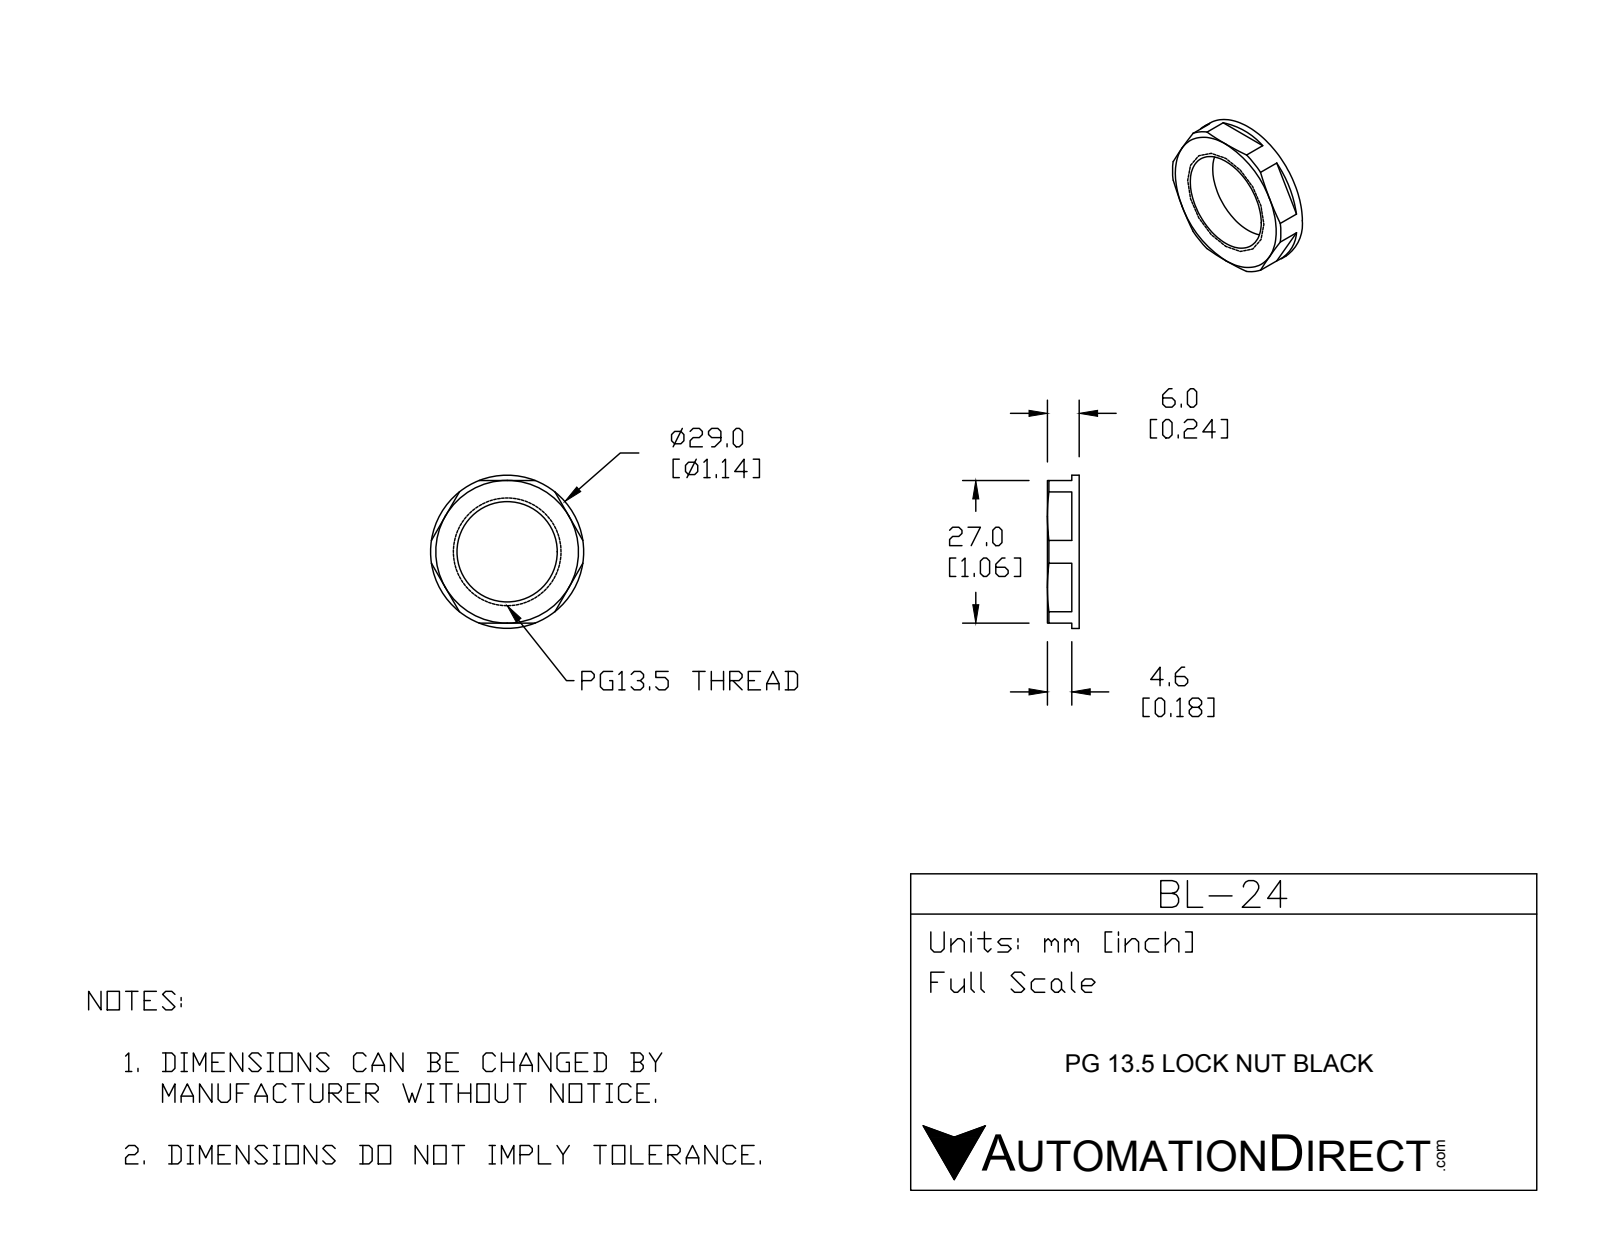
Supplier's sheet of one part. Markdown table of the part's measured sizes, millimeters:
| quantity | value |
| --- | --- |
| part name | BL-24 |
| STEP written by | SolidWorks 2015 (CONFIG_CONTROL_DESIGN) |
| units | millimeters |
| bodies | 1 solid, 33 faces (17 planar, 10 cylindrical, 6 other) |
| overall size | 29 × 29 × 6 |
| volume | 2 059 mm³ |
| surface area | 1 645 mm² |
| round holes (diameter × count) | 1.5 × 3, 19 × 1 |
| round bosses / shafts (diameter × count) | 29 × 1 |
| main face-to-face distances | 6, 27, 1.4, 4.6, 1.1, 5.7 |
| hole center spacings | 13.05, 22.6, 22.61 |
